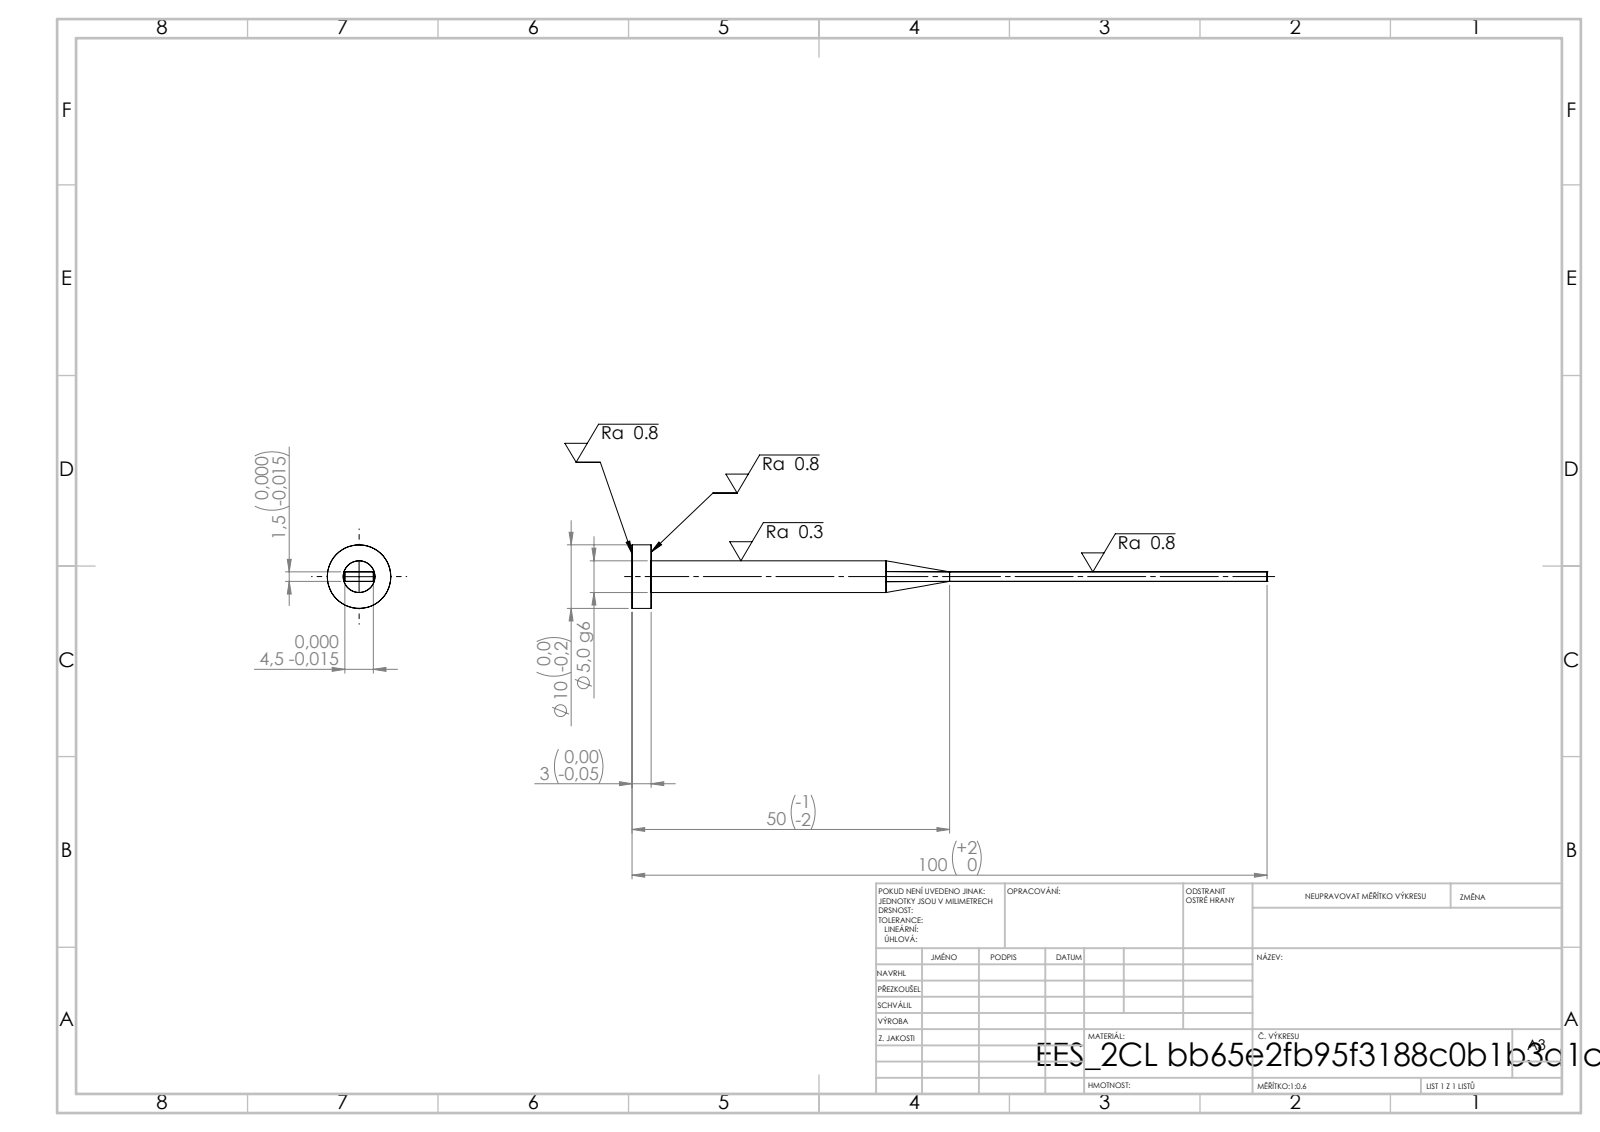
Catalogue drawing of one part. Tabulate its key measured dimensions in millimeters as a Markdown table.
| quantity | value |
| --- | --- |
| STEP written by | SolidWorks 2019 (CONFIG_CONTROL_DESIGN) |
| units | millimeters |
| bodies | 1 solid, 15 faces (7 planar, 4 cylindrical, 4 other) |
| overall size | 100 × 10 × 10 |
| volume | 1 427 mm³ |
| surface area | 1 554 mm² |
| round bosses / shafts (diameter × count) | 10 × 1, 5 × 1 |
| main face-to-face distances | 1.5, 4.5, 3, 100, 97 |
